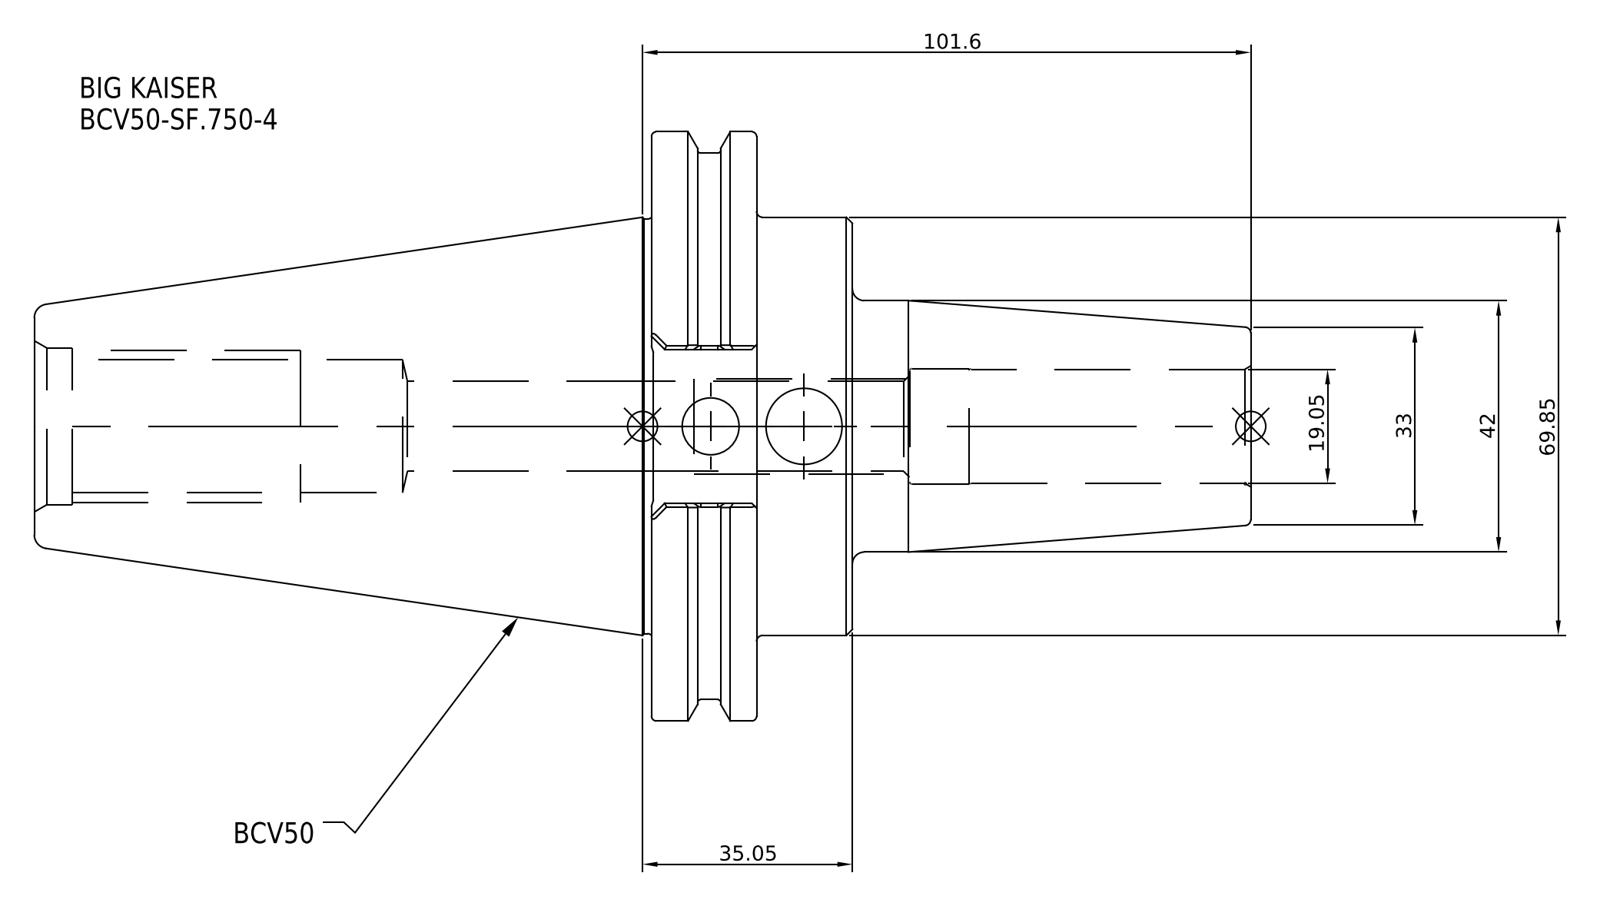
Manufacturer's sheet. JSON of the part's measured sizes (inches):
{"part_name": "BCV50-SF_750-4", "step_written_by": "SolidWorks 2021 (CONFIG_CONTROL_DESIGN)", "units": "inches", "bodies": {"solids": 1, "faces": 30, "planar": 8, "cylindrical": 14, "other": 8}, "overall_size": [8, 3.875, 3.875], "volume_in3": 30.86, "surface_area_in2": 79.45, "round_holes": [[0.75, 1]], "round_bosses_or_shafts": [[3.875, 1], [3.594, 1], [2.75, 1], [1.654, 1]], "face_to_face_distances": [0.691, 0.63, 1.321, 5.38, 4.75, 4.059, 2.62, 3.25, 3.941, 8]}
